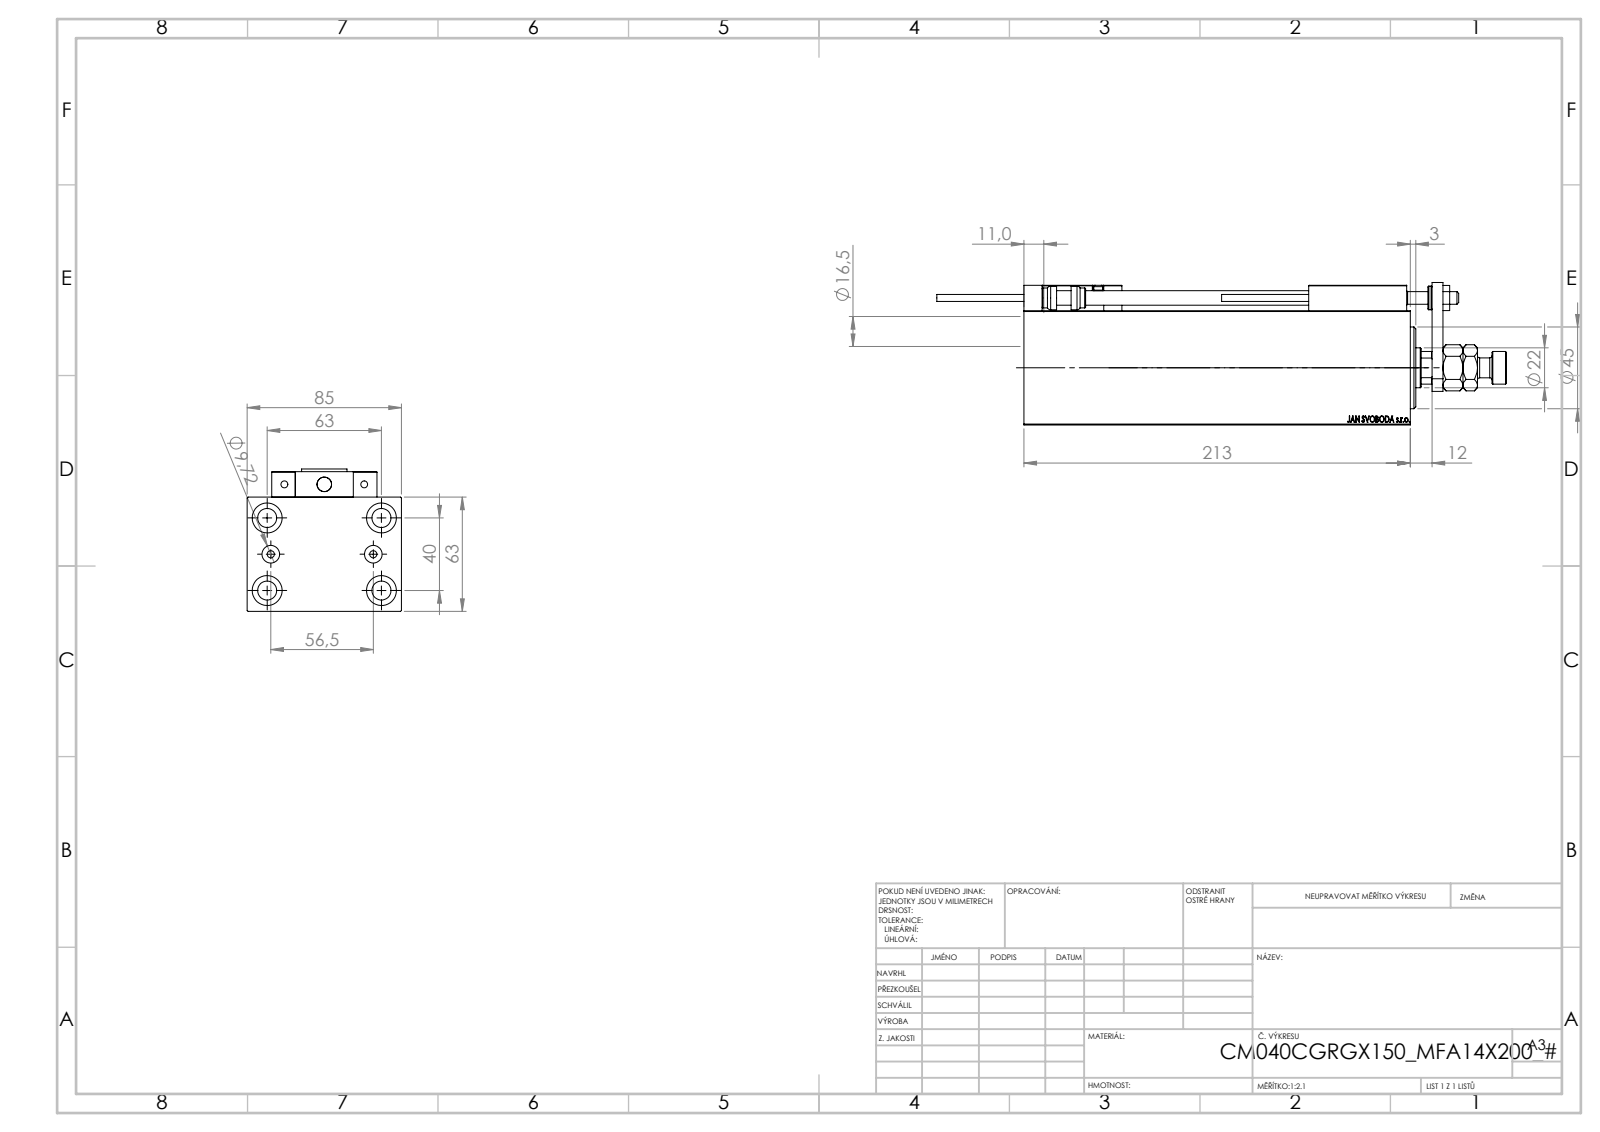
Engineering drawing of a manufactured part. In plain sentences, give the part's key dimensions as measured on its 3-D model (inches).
The part is named "NUT_D12; ALLEN BOLT D5; KONCOVKA; SWITCH DIM B,W (+7 more)". Its 3-D file was written by "SolidWorks 2019 (CONFIG_CONTROL_DESIGN)". It is 24 solids with 1330 faces: 576 planar, 188 cylindrical and 566 other. Overall it measures 12.323 by 3.346 by 3.091 inches. Its volume is 67.74 cubic inches and its surface area 250.8 square inches. Round holes: 6 of diameter 0.157, 5 of diameter 0.315, 5 of diameter 0.65, 4 of diameter 0.126, 4 of diameter 0.413, 2 of diameter 0.197, 2 of diameter 0.383, 1 of diameter 0.276, 1 of diameter 0.492, 1 of diameter 0.866, 1 of diameter 1.004, 1 of diameter 1.575. Round bosses or shafts: 2 of diameter 0.433, 2 of diameter 0.197, 2 of diameter 0.15, 1 of diameter 0.709, 1 of diameter 0.512. Partial cylindrical surfaces (rounded edges, fillets, slot ends): 30 of radius 0.012, 2 of radius 0.118, 1 of radius 0.413. The main face-to-face distances are 2.48, 3.346, 0.551, 8.386, 2.008, 6.378, 0.433, 0.394, 3.031, 0.236. The hole center spacings are 0.798, 1.469, 2.481, 0.448, 0.787, 1.112, 1.165, 1.169.
